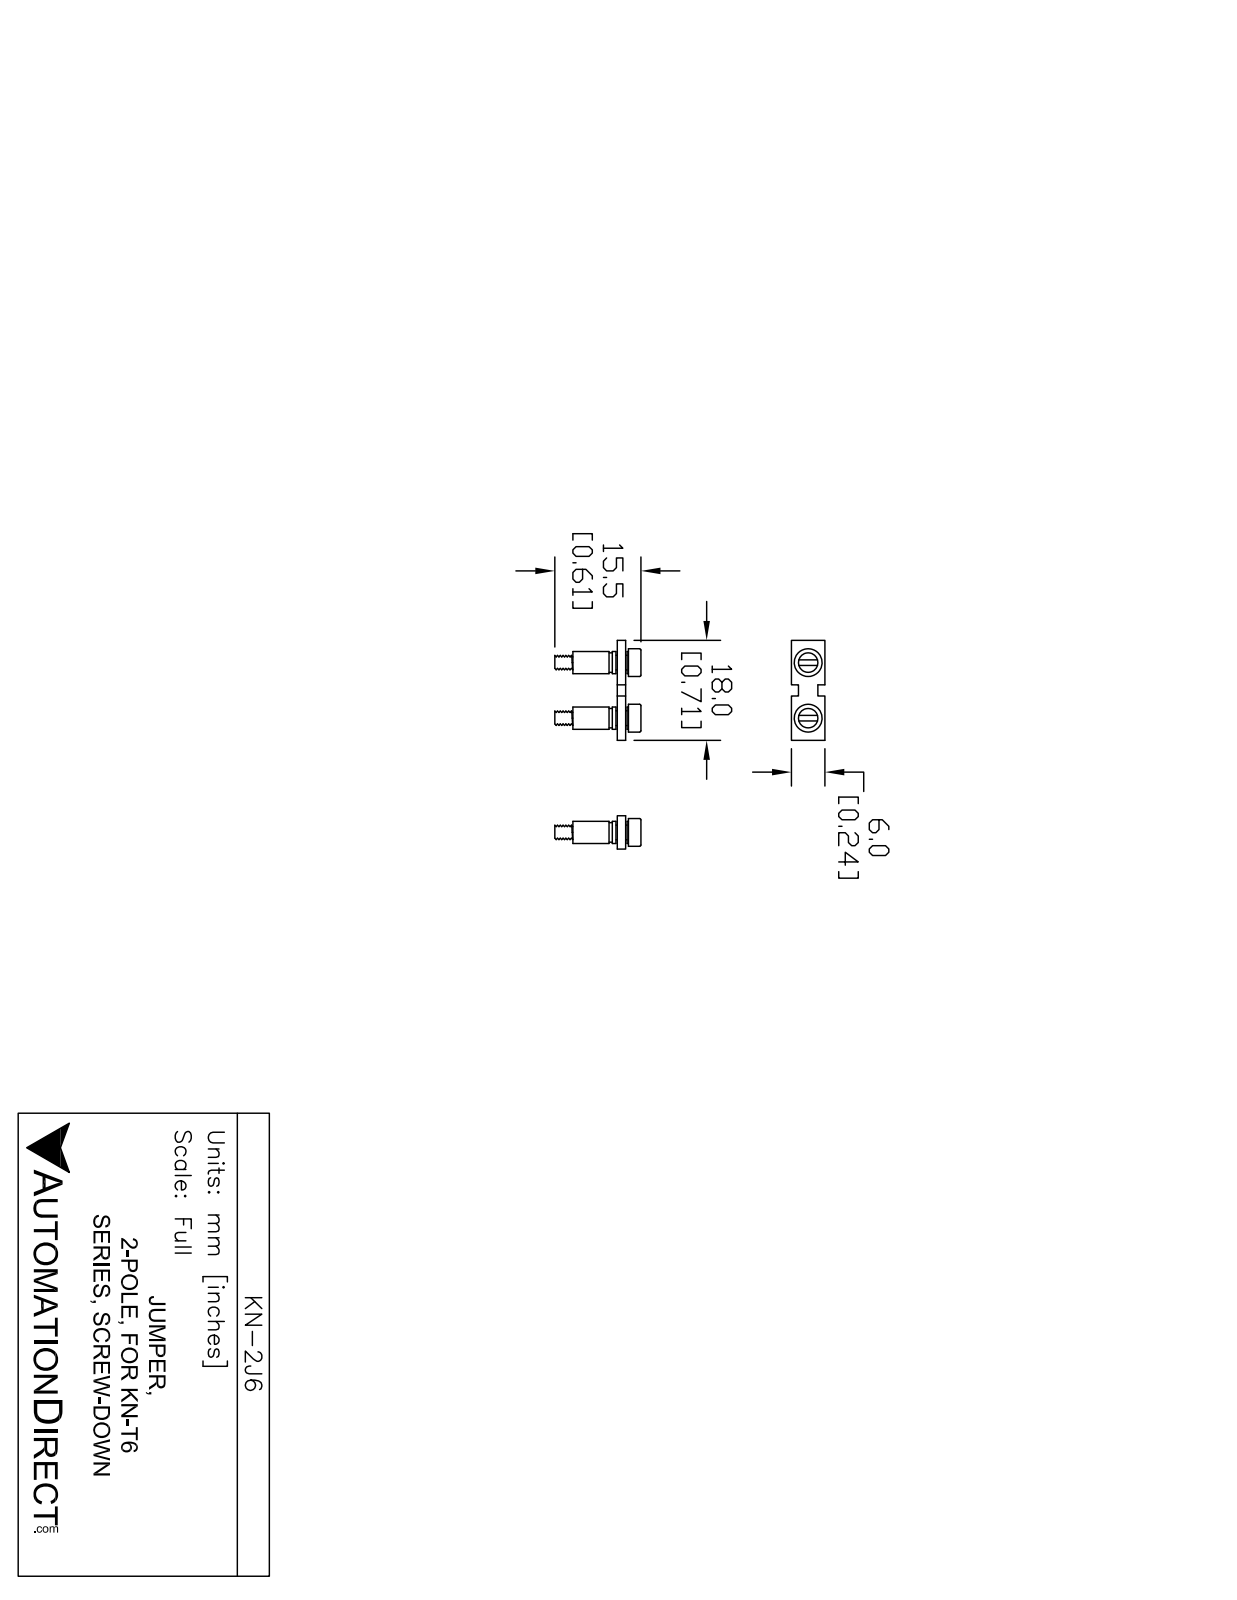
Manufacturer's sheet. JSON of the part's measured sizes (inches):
{"part_name": "KN-2J6", "step_written_by": "SolidWorks 2014 (AUTOMOTIVE_DESIGN)", "units": "inches", "bodies": {"solids": 7, "faces": 100, "planar": 46, "cylindrical": 42, "other": 12}, "overall_size": [0.709, 0.61, 0.236], "volume_in3": 0.026, "surface_area_in2": 1.804, "round_holes": [[0.11, 2], [0.118, 2], [0.124, 2], [0.138, 2]], "round_bosses_or_shafts": [[0.197, 2], [0.157, 2], [0.104, 2]], "face_to_face_distances": [0.059, 0.079, 0.069, 0.089, 0.02, 0.177, 0.394, 0.236, 0.138, 0.039], "hole_center_spacings": [0.394]}
